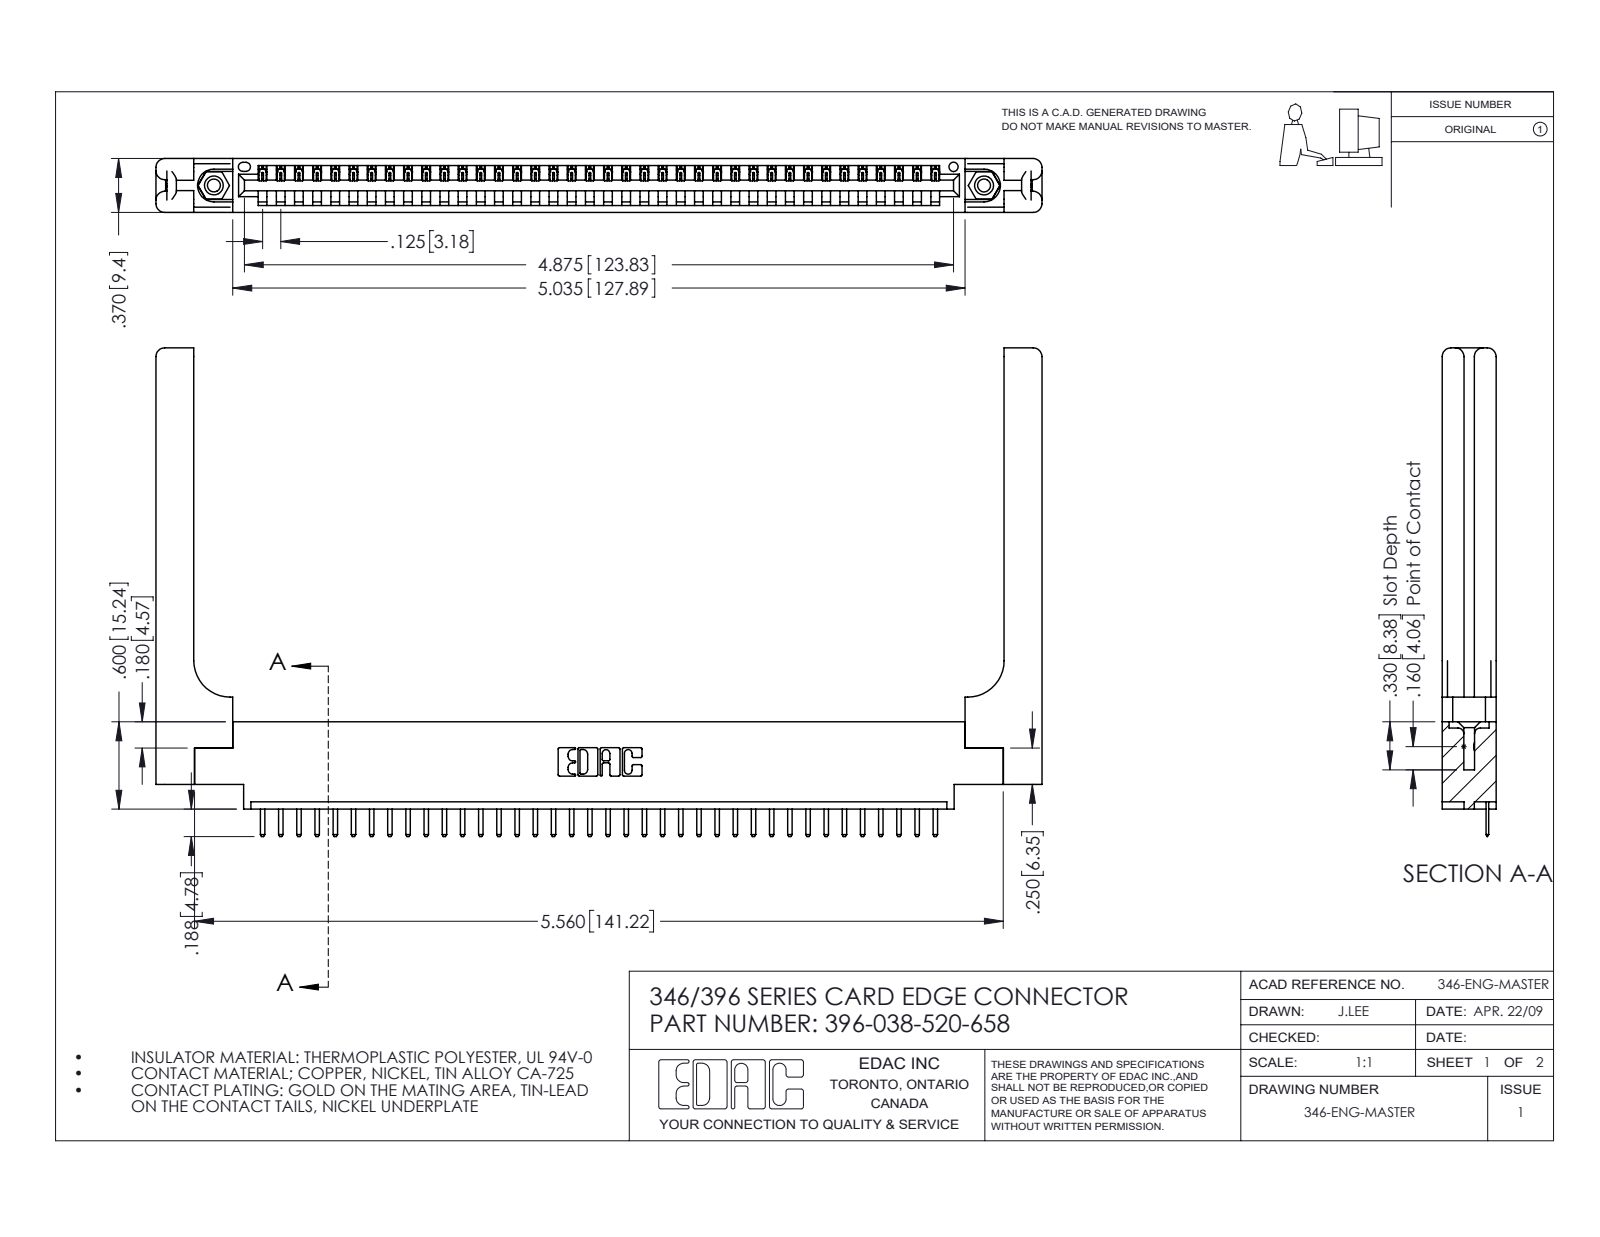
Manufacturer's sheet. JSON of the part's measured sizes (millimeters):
{"part_name": "396-038-520-658; 345-292-001_345-293-120; 345-250-001_345-250-001-102; 346 Part_0.170 Offset - 0.156 Dia-TH (+1 more)", "step_written_by": "SolidWorks 2016 (CONFIG_CONTROL_DESIGN)", "units": "millimeters", "bodies": {"solids": 43, "faces": 2738, "planar": 1824, "cylindrical": 854, "other": 60}, "overall_size": [154.7, 85.3, 9.4], "volume_mm3": 22040, "surface_area_mm2": 23060, "round_holes": [[2.3, 2], [3.2, 2], [4, 2], [1.6, 1]], "round_bosses_or_shafts": [[3.9, 2]], "partial_cylinders_radius": [[0.3, 78], [0.2, 76], [0.3, 22], [1.5, 16], [0.2, 6], [0.8, 6], [0.7, 3], [0.8, 2]], "face_to_face_distances": [9.4, 1.2, 8.2, 1.8, 3.8, 3.8, 6.4, 7.6, 0.6, 5.6], "hole_center_spacings": [6.2, 129.2, 134.5]}
